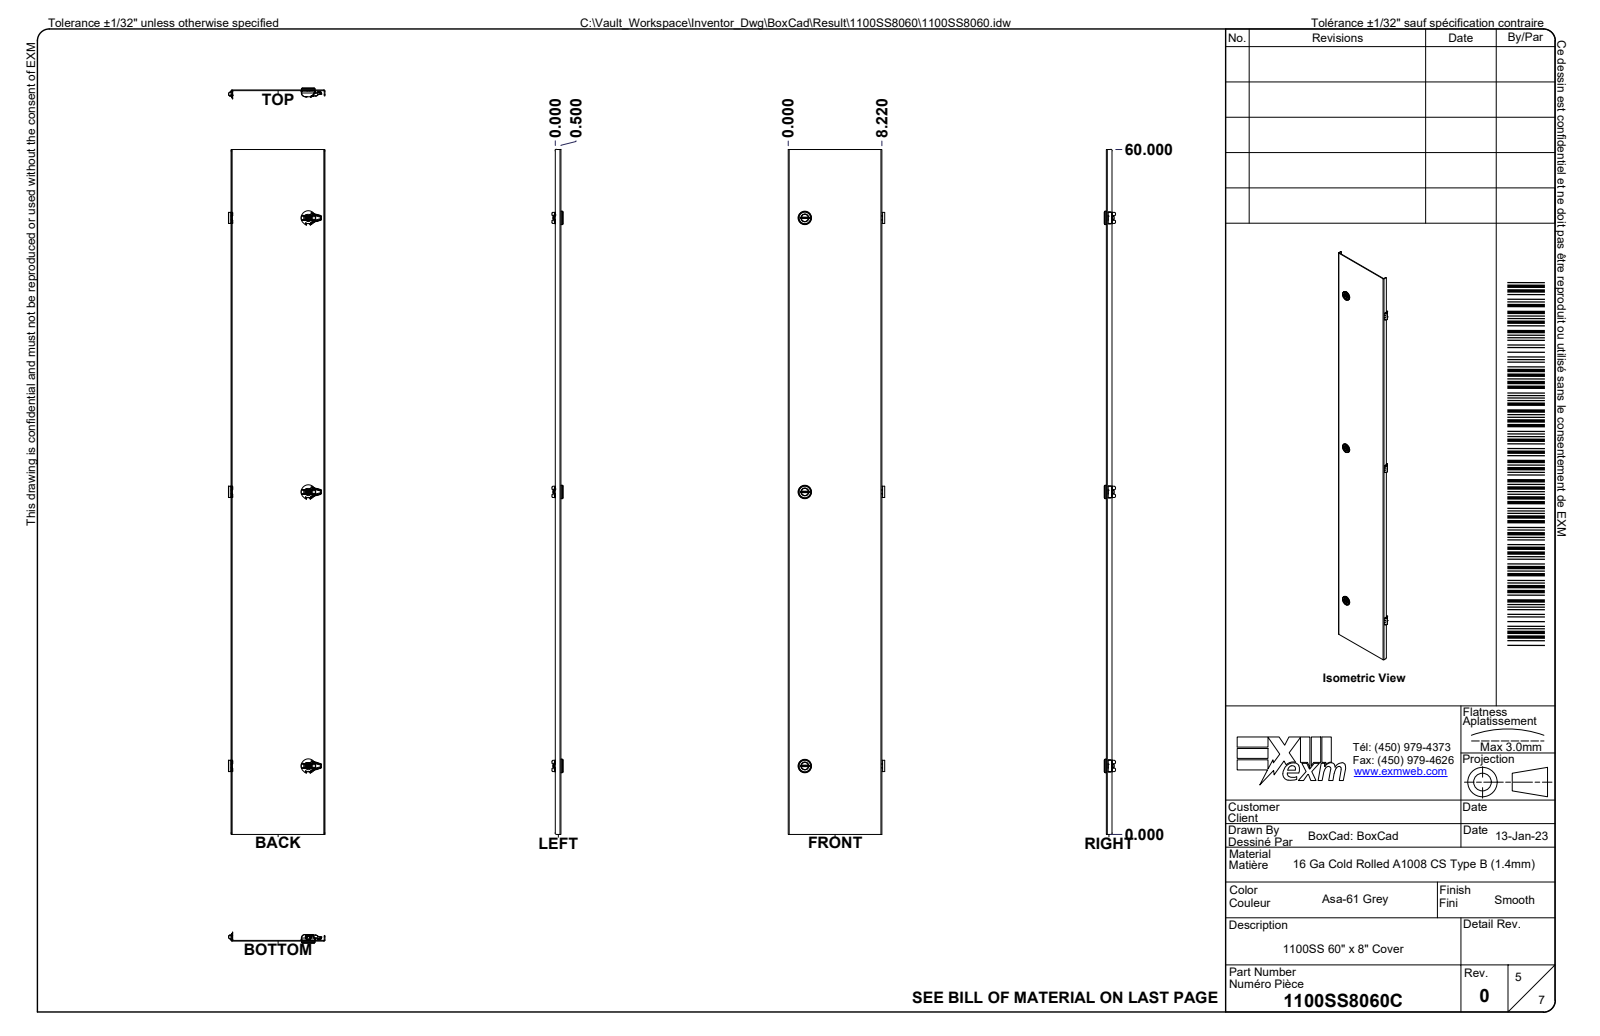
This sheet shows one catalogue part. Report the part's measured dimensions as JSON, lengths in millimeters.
{"part_name": "1100SS8060; 1100SS8060B; 1100SS8060B-P; 1100SS8060C (+8 more)", "step_written_by": "Autodesk Inventor 2024 (AUTOMOTIVE_DESIGN)", "units": "millimeters", "bodies": {"solids": 11, "faces": 5090, "planar": 1929, "cylindrical": 1367, "other": 1794}, "overall_size": [1524, 213.5, 209.2], "volume_mm3": 1848000, "surface_area_mm2": 2653000, "round_holes": [[7.1, 12], [22.2, 5], [28.6, 5], [0.8, 3]], "round_bosses_or_shafts": [[28.6, 5], [22.2, 5], [32, 3], [30, 3], [20, 3]], "partial_cylinders_radius": [[0.3, 557], [0.5, 55], [2, 30], [0.2, 19], [1, 10], [0.6, 9], [0.1, 6], [0.2, 6]], "face_to_face_distances": [1.4, 201.8, 203.2, 200.4, 204.6, 2.8, 2.8, 4.2, 204.6, 206], "hole_center_spacings": [152.4, 50.8, 160.6, 304.8, 1447.8, 1455.8, 1498.6, 1506.3]}
